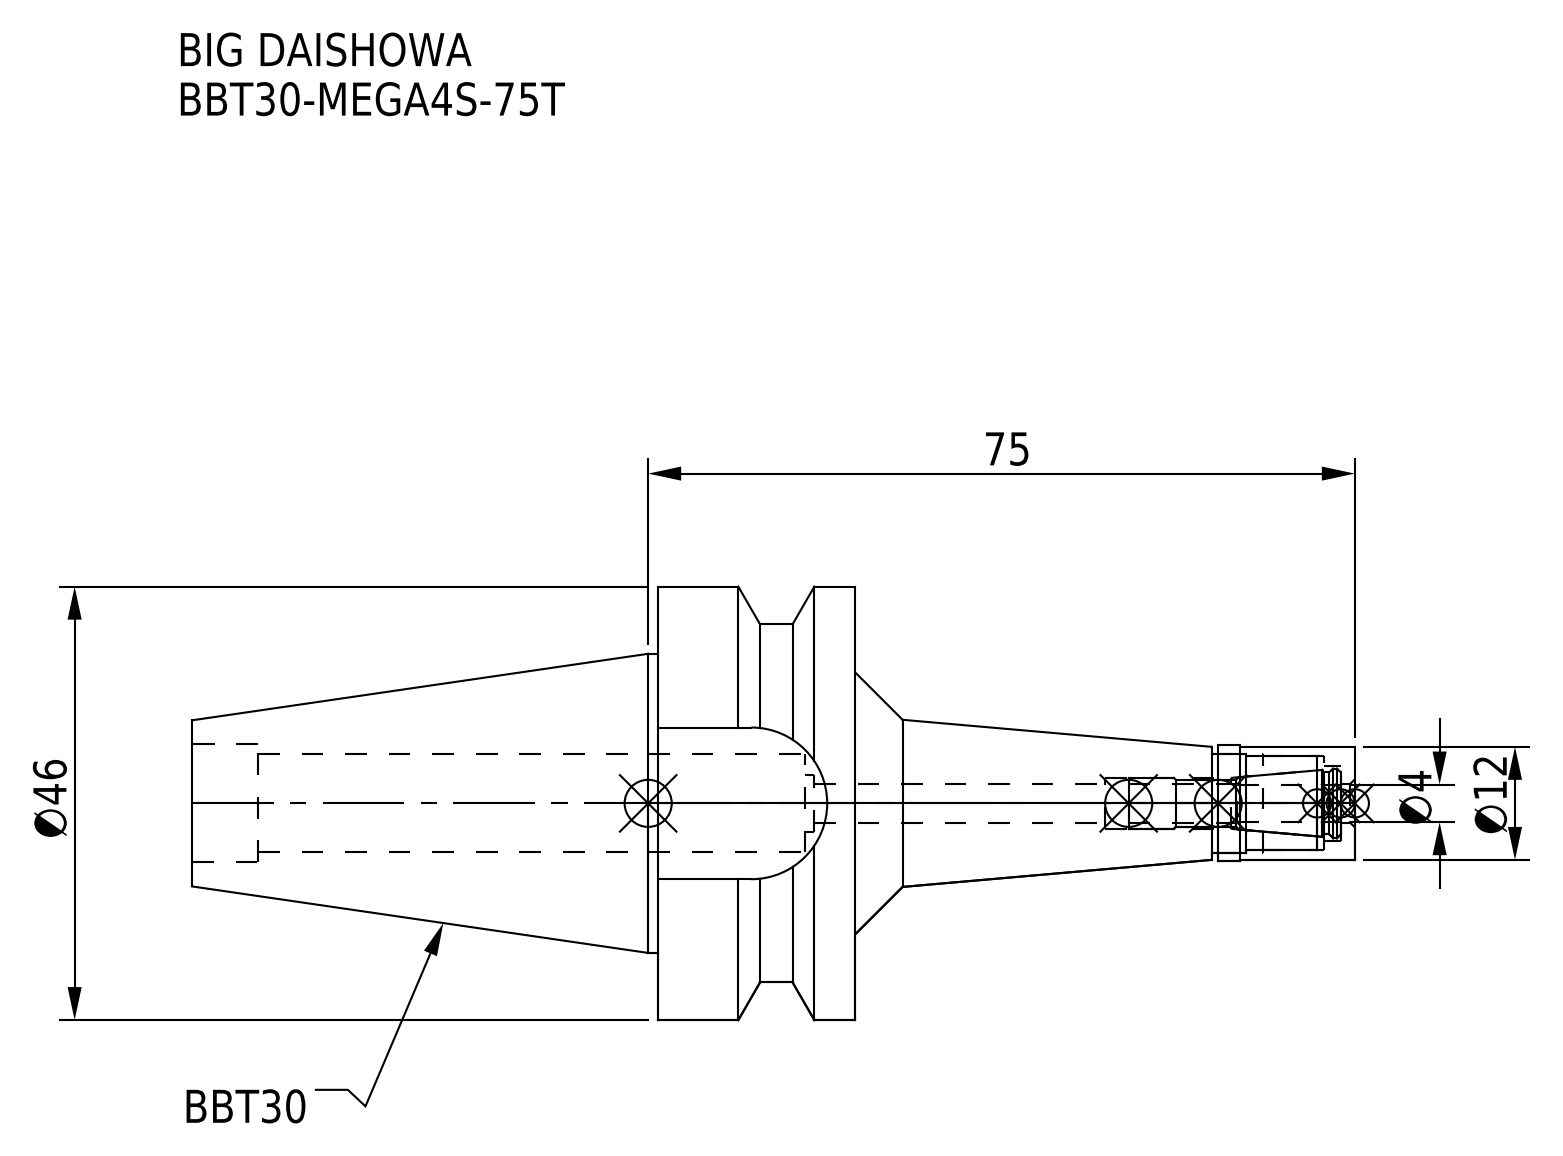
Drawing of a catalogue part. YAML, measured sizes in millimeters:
part_name: "BBT30-MEGA4S-75T; BBT30-MEGA4S-75T_1.stp; DXF_TEMP_ASSY_ASM_4_ASM.stp; MGN4S_1.stp (+3 more)"
step_written_by: "SolidWorks 2019 (CONFIG_CONTROL_DESIGN)"
units: millimeters
bodies: {solids: 2, faces: 74, planar: 22, cylindrical: 38, other: 14}
overall_size: [123.4, 46, 46]
volume: 56366
surface_area: 16279
round_holes:
  - {diameter: 4.1, count: 1}
  - {diameter: 4.2, count: 1}
  - {diameter: 5.4, count: 1}
  - {diameter: 6, count: 1}
  - {diameter: 8, count: 1}
  - {diameter: 10, count: 1}
  - {diameter: 10.4, count: 1}
  - {diameter: 10.5, count: 1}
  - {diameter: 12.5, count: 1}
round_bosses_or_shafts:
  - {diameter: 46, count: 1}
  - {diameter: 31.75, count: 1}
  - {diameter: 12.3, count: 1}
  - {diameter: 12, count: 1}
partial_cylinders:
  - {radius: 8.05, count: 1}
  - {radius: 19, count: 1}
face_to_face_distances: [21, 32.6, 70.4, 49.4, 16.1, 53, 74, 123.4, 0.7, 58.4]
